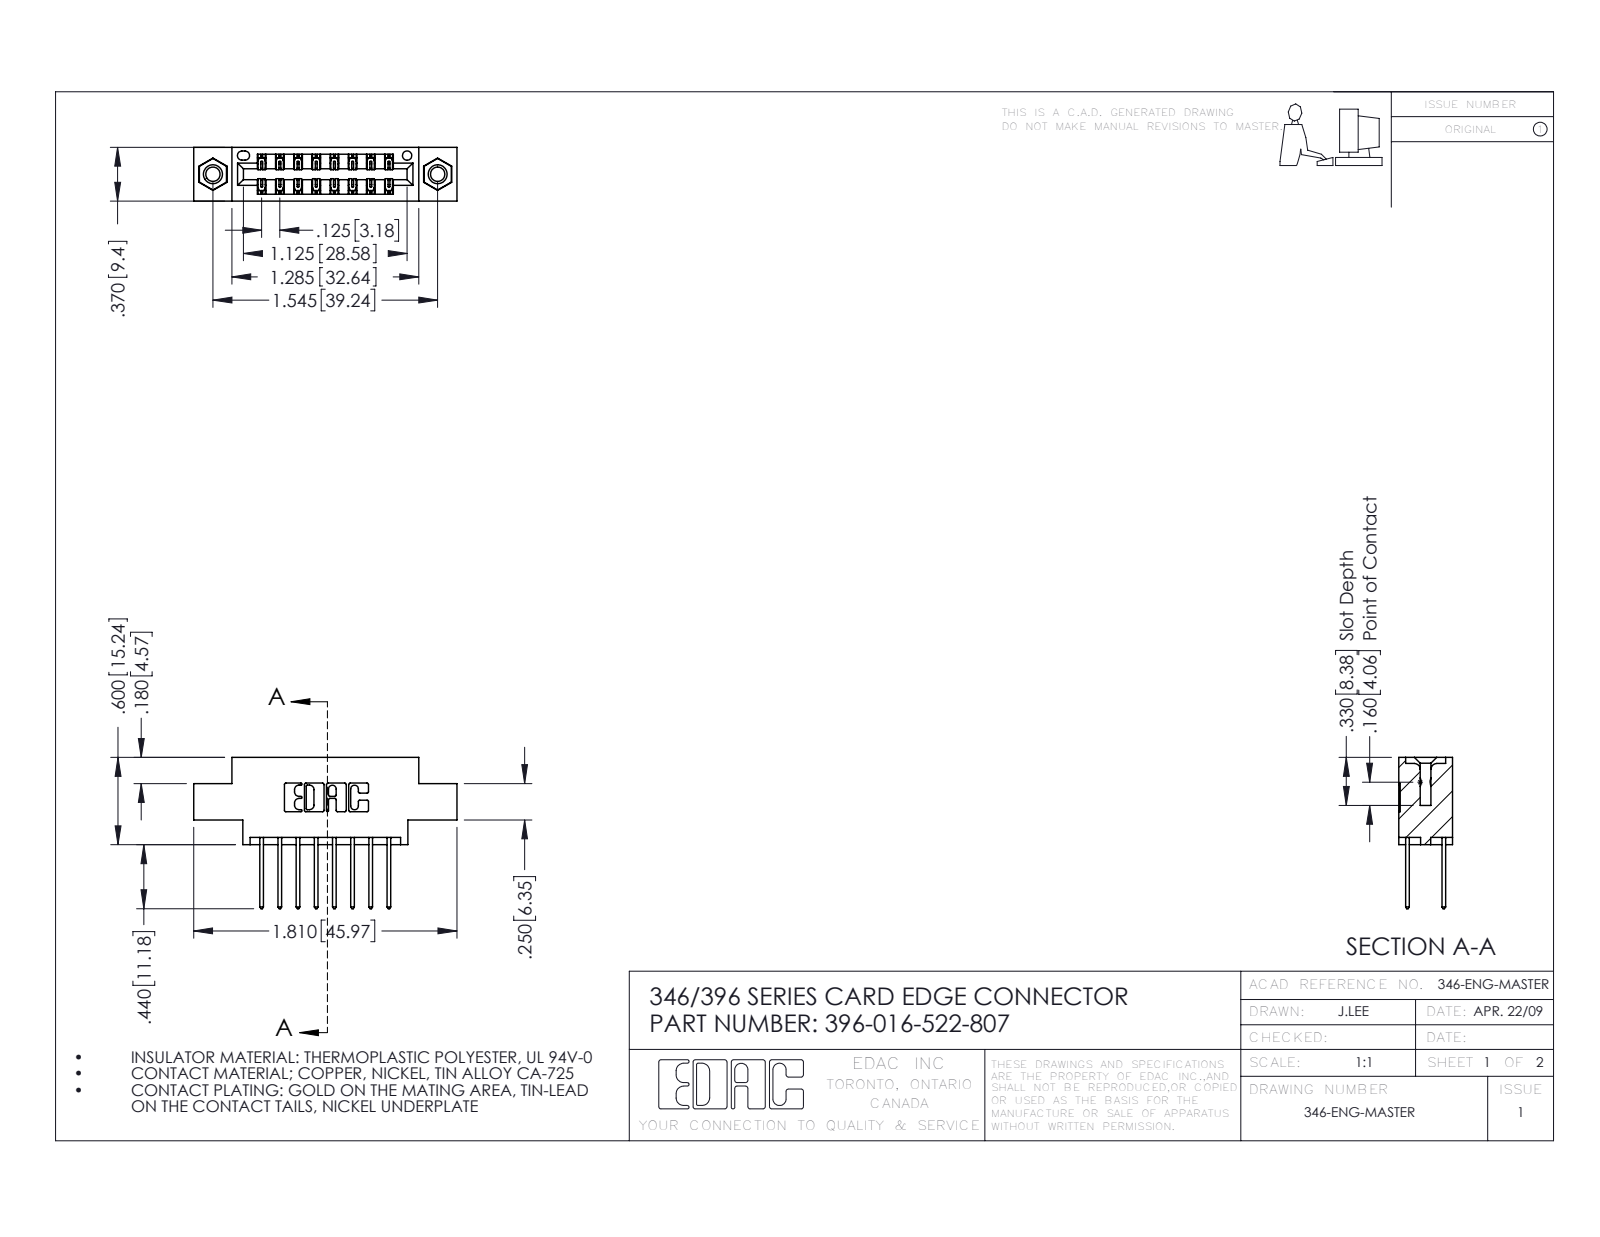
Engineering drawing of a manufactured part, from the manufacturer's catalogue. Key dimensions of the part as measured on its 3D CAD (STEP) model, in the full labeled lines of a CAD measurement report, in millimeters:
Part name (STEP PRODUCT): 345-292-001_345-293-122; 345-250-001_345-250-005-103; 396-016-522-807; 346 Part_0.170 Offset - 0.156 Dia-TI
STEP written by: SolidWorks 2016 (CONFIG_CONTROL_DESIGN)
Units: millimetres
Bodies: 19 solids, 1018 faces (672 planar, 330 cylindrical, 16 other)
Overall size (bounding box): 46 × 26.4 × 9.4
Volume: 4 100 mm³ · Surface area: 5 494 mm²
Round holes (diameter × count): ⌀2.5 ×2, ⌀3.2 ×2, ⌀4 ×2, ⌀1.6 ×1
Round bosses / shafts (diameter × count): ⌀3.9 ×2
Partial cylindrical surfaces — rounded edges, fillets, slot ends (radius × count): R0.2 ×24, R0.3 ×22, R0.3 ×16, R0.2 ×6, R0.8 ×6, R0.7 ×3, R0.4 ×2, R0.6 ×2
Main face-to-face distances: 6.4, 1.2, 8.2, 9.4, 1.8, 7.6, 0.6, 7, 5.6, 3.8
Hole centre spacings: 6.2, 34.1, 39.2
